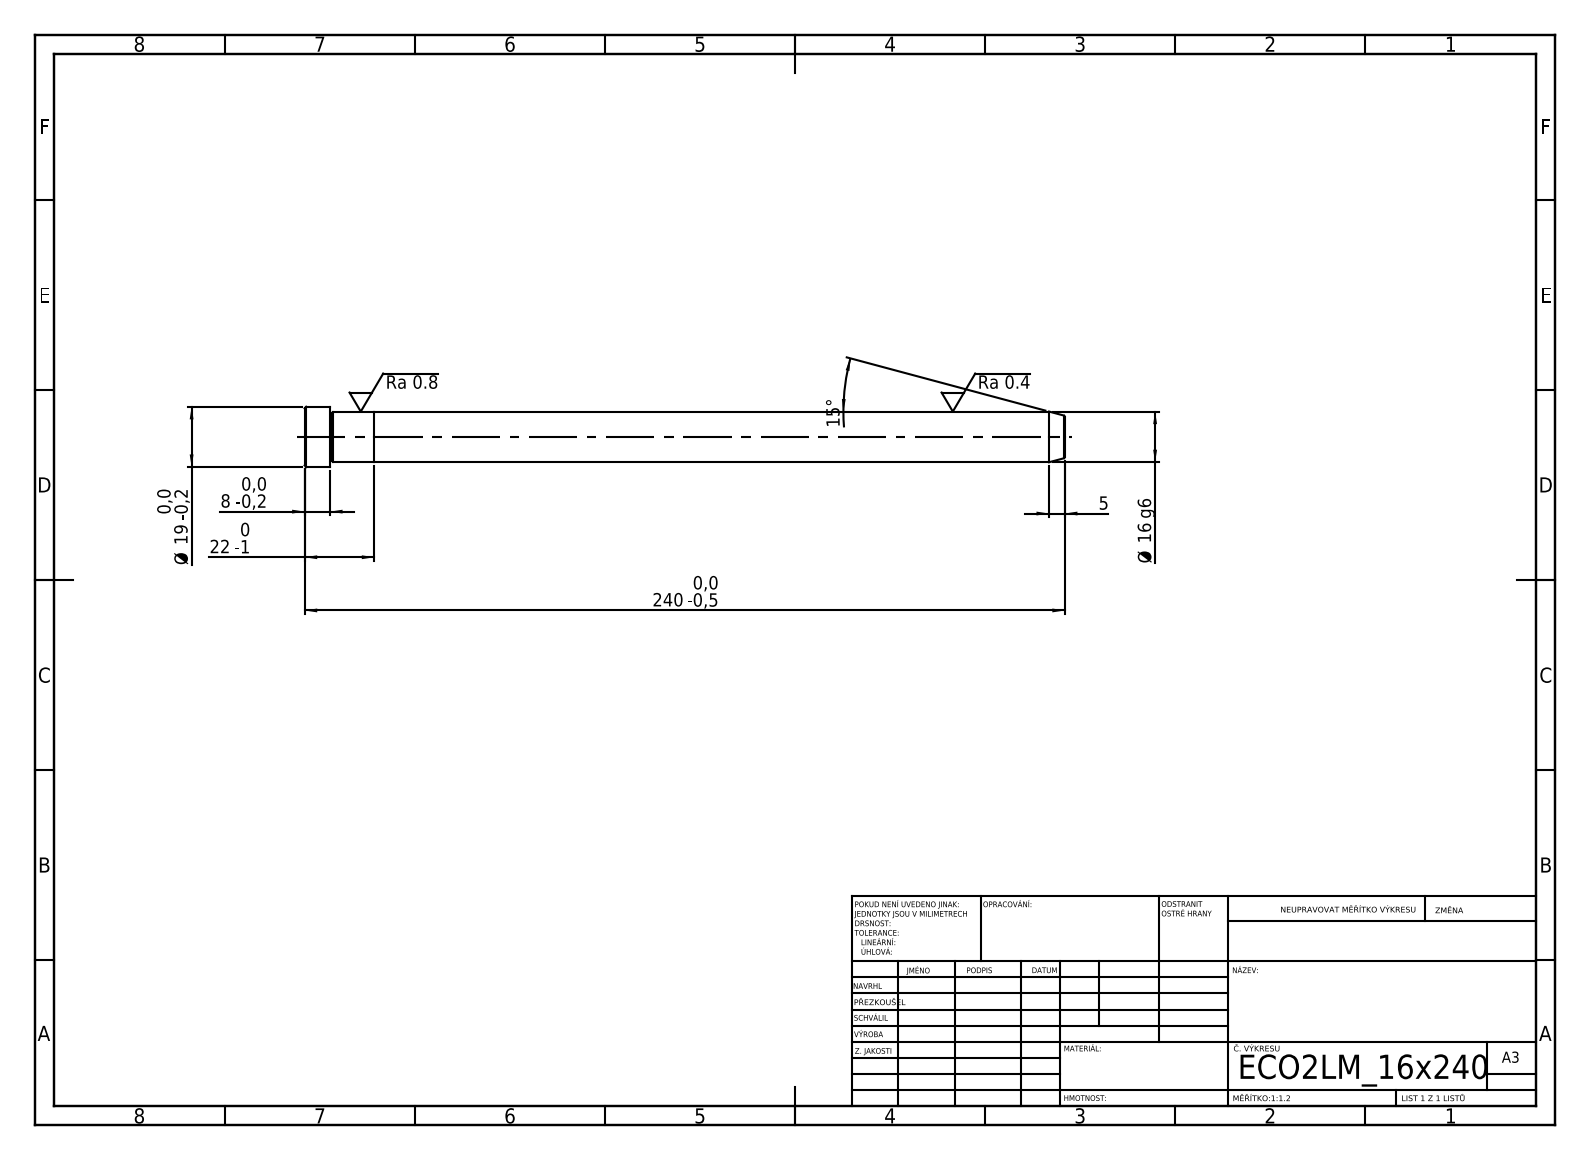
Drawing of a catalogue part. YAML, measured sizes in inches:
step_written_by: "SolidWorks 2019 (CONFIG_CONTROL_DESIGN)"
units: inches
bodies: {solids: 2, faces: 21, planar: 5, cylindrical: 6, other: 10}
overall_size: [9.449, 0.748, 0.748]
volume: 2.974
surface_area: 20.21
round_bosses_or_shafts:
  - {diameter: 0.748, count: 1}
  - {diameter: 0.63, count: 1}
face_to_face_distances: [0.866, 8.583, 9.449, 9.134, 0.551, 0.315]
